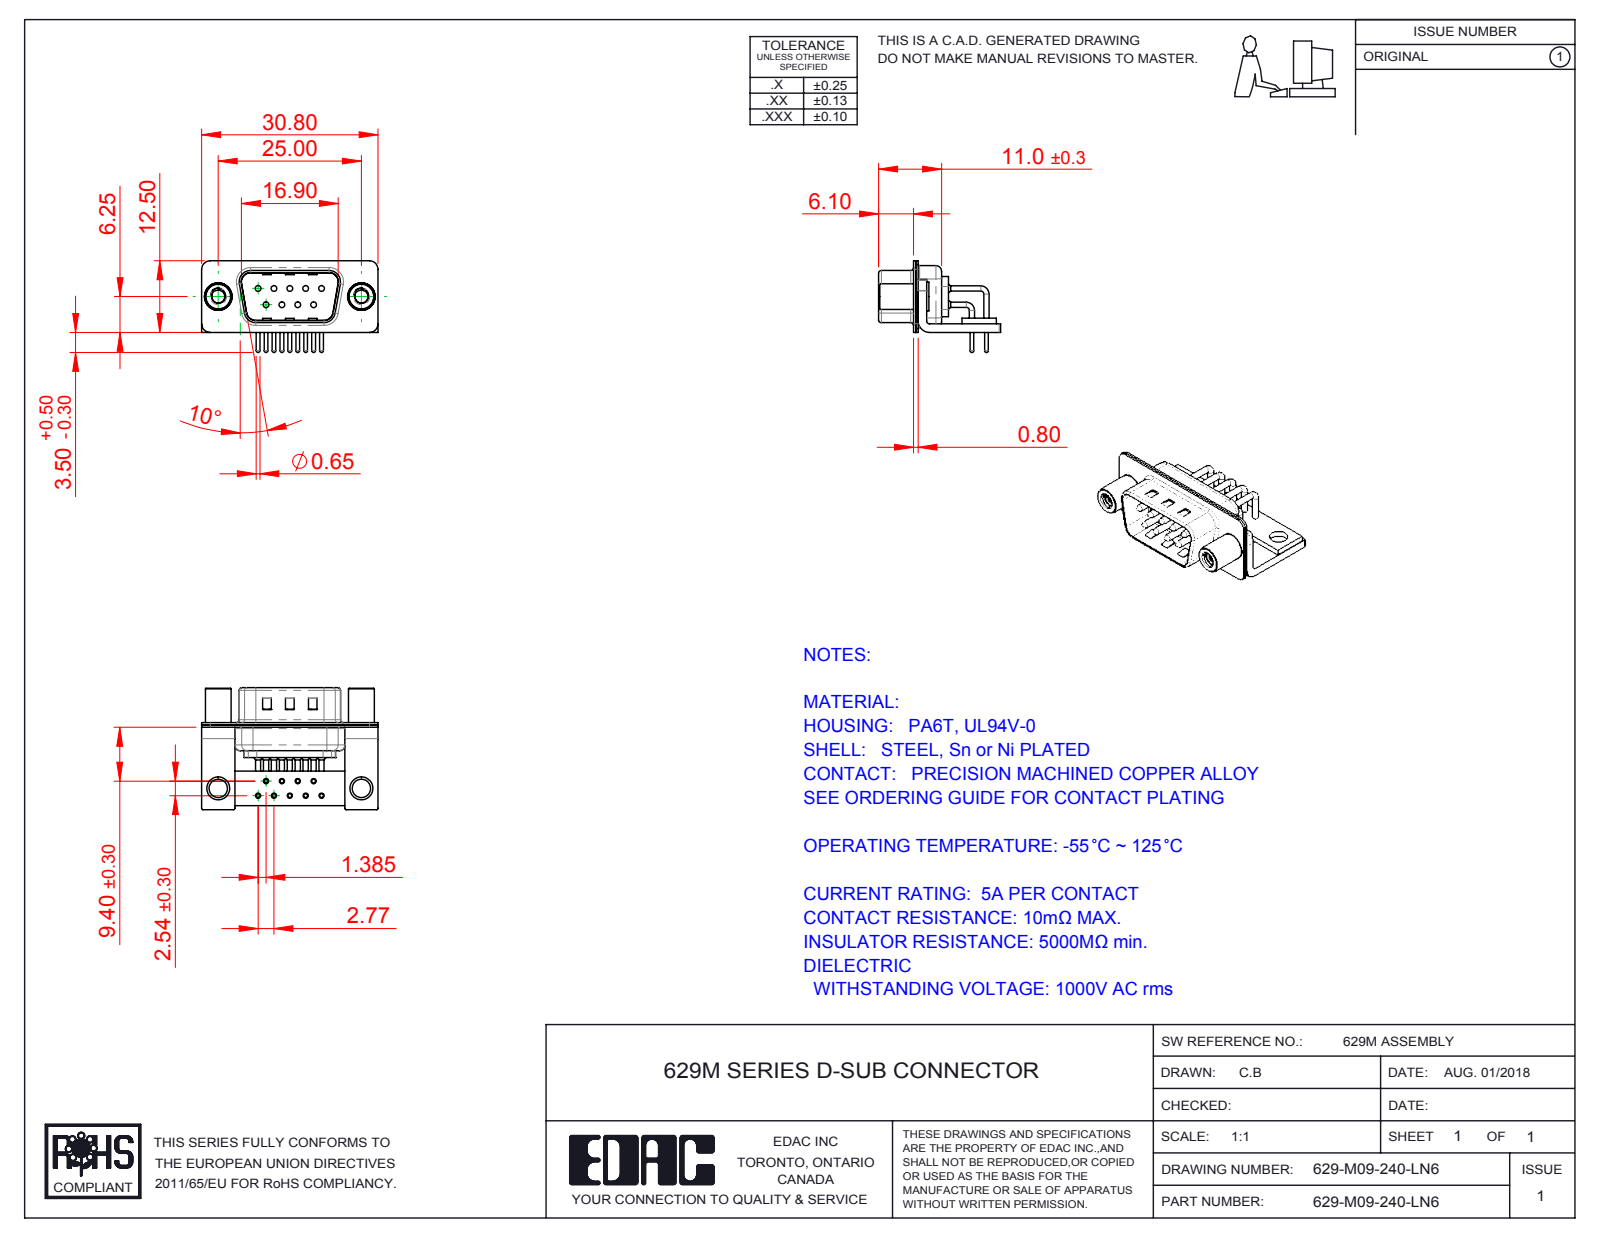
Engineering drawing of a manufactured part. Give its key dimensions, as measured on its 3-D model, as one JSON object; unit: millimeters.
{"part_name": "629M Stabilizer Board_09 Contacts; 629M 4-40 Threaded Standoff; 629M Stabilizer Bracket; 629M Contact Row 2 (+5 more)", "step_written_by": "SolidWorks 2016 (CONFIG_CONTROL_DESIGN)", "units": "millimeters", "bodies": {"solids": 17, "faces": 1412, "planar": 711, "cylindrical": 535, "other": 166}, "overall_size": [30.8, 21.3, 16], "volume_mm3": 1938, "surface_area_mm2": 5267, "round_holes": [[0.9, 9], [1, 9], [1.7, 9], [2, 9], [2.26, 2], [3.2, 2], [4, 2], [4.8, 2]], "round_bosses_or_shafts": [[1.5, 9], [0.9, 9], [0.65, 9], [5, 2], [4.9, 2], [4.5, 2]], "partial_cylinders_radius": [[0.25, 16], [1.5, 16], [2, 13], [0.5, 9], [1.01, 9], [1.6, 8], [0.6, 4], [0.65, 4]], "face_to_face_distances": [0.4, 1.5, 0.8, 0.85, 1.25, 1.9, 1, 2.5, 10.4, 9.55], "hole_center_spacings": [2.77, 5.54, 3.16, 4.87, 8.31, 2.89, 2.9, 5.03]}
